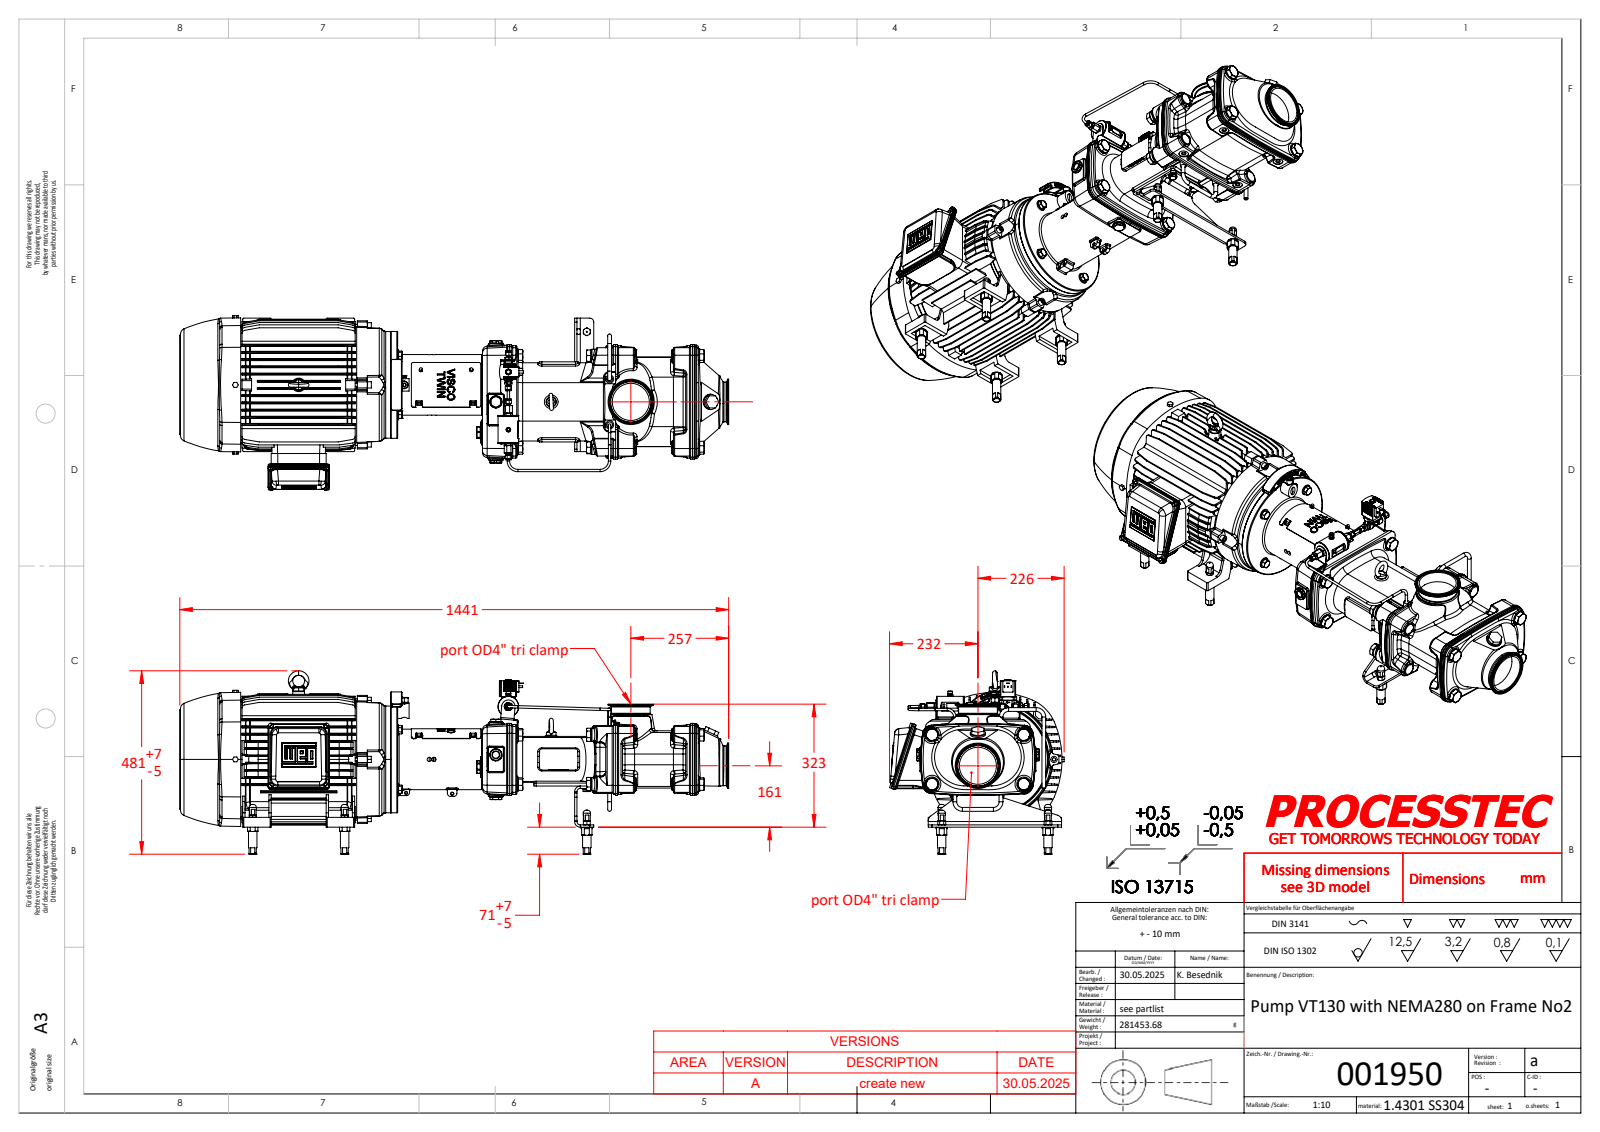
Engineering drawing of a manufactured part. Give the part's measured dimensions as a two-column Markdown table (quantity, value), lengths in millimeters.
| quantity | value |
| --- | --- |
| part name | LA Socket Set Screw ISO-4029 M12x20 A2_ISO 4029 - M12 X 20; 001076; 001539; 001074 (+8 more) |
| STEP written by | SolidWorks 2023 (AUTOMOTIVE_DESIGN) |
| units | millimeters |
| bodies | 135 solids, 9815 faces (3241 planar, 2255 cylindrical, 4319 other) |
| overall size | 1441 × 481.3 × 458.07 |
| volume | 70 880 000 mm³ |
| surface area | 4 286 000 mm² |
| round holes (diameter × count) | 10.2 × 11, 8.5 × 10, 17.5 × 9, 6.8 × 8, 10.5 × 8, 17 × 8, 6 × 7, 8 × 7, 5.9 × 6, 7.2 × 6, 8.2 × 6, 12 × 6 |
| round bosses / shafts (diameter × count) | 6 × 13, 8 × 12, 10 × 11, 30 × 10, 5 × 8, 22 × 7, 20 × 6, 19 × 6 |
| partial cylindrical surfaces (radius × count) | 2 × 120, 3 × 107, 4 × 83, 0.5 × 60, 8 × 43, 1.5 × 33, 7 × 27, 5 × 25 |
| main face-to-face distances | 481, 189.19, 305, 786, 18.67, 132.27, 165.28, 5.24, 150.94, 170.52 |
| hole center spacings | 51, 129.3, 55, 62.81, 113.29, 139.08, 168.03, 241.3 |
